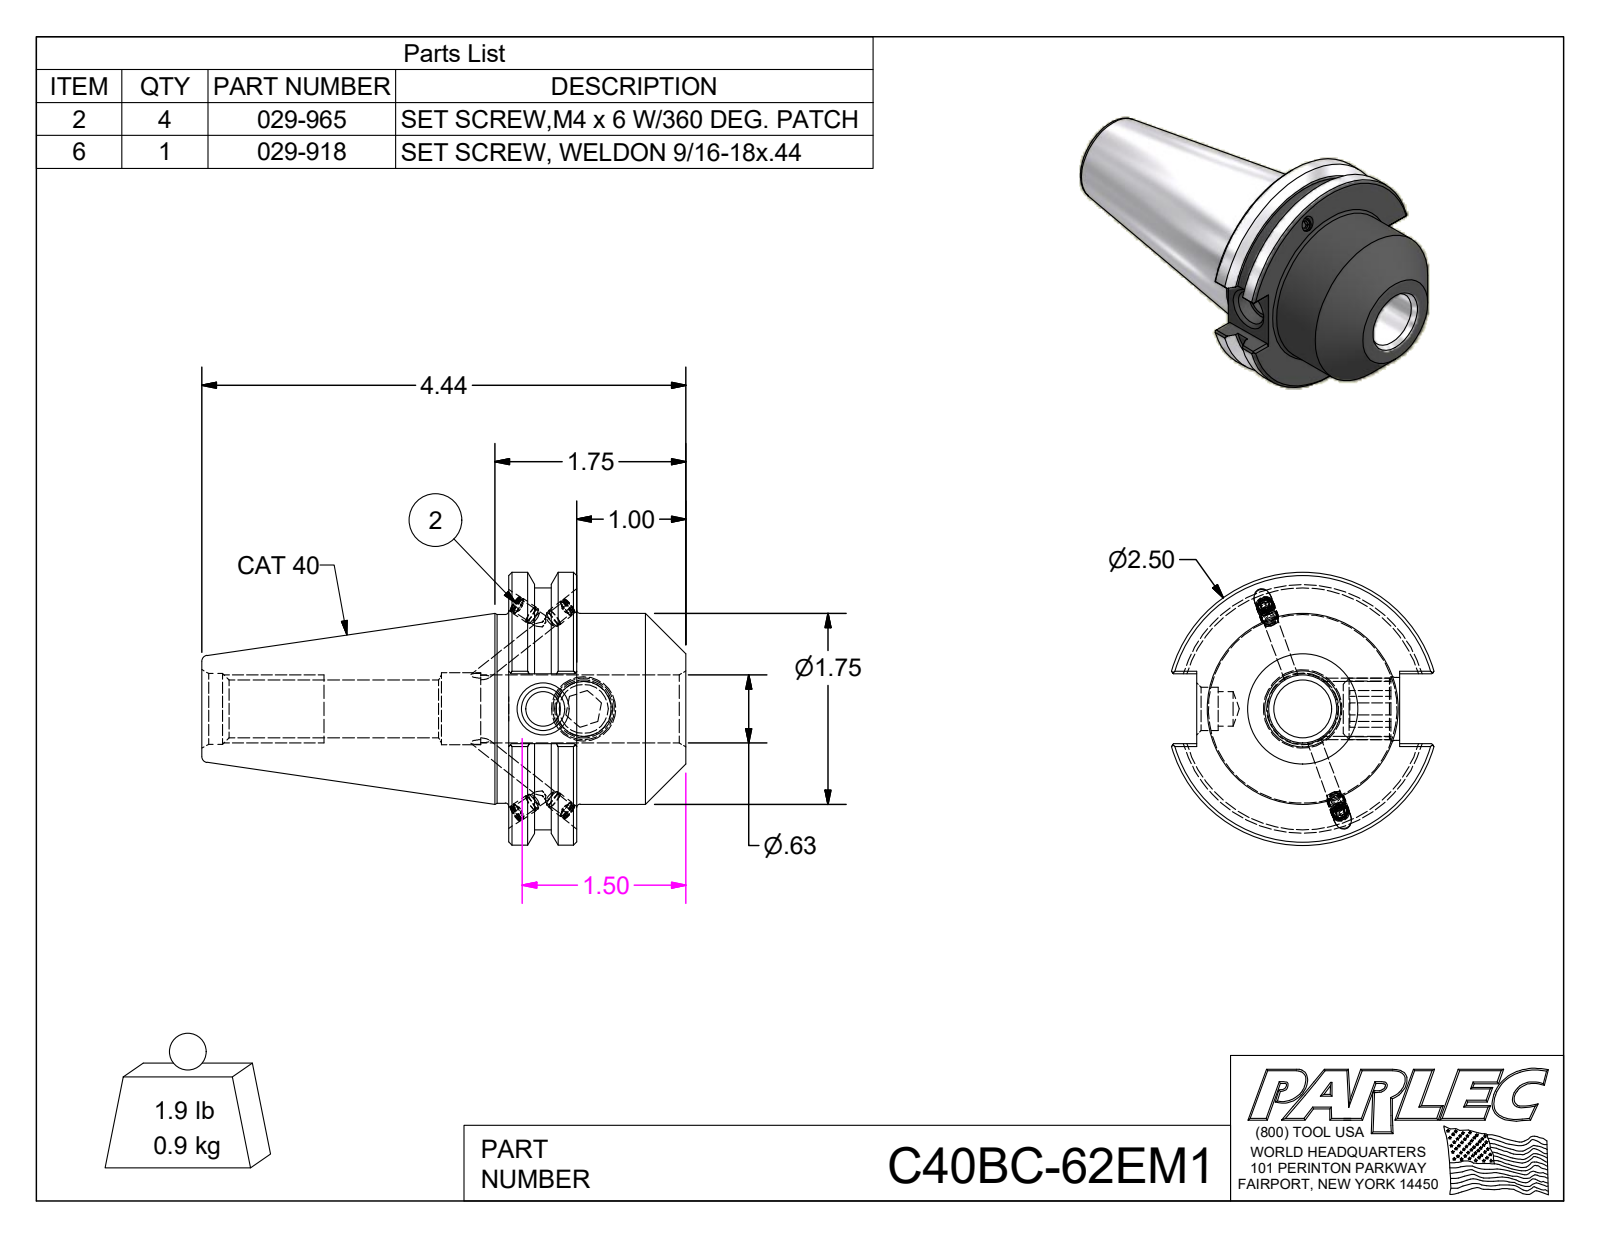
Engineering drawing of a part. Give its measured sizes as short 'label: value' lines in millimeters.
name: C40BC-62EM1; C40BC-62EM1-1; 029-918; 029-965
written by: Autodesk Inventor 2012 (AUTOMOTIVE_DESIGN)
unit: mm
bodies: 6 solids, 167 faces (87 planar, 36 cylindrical, 44 other)
size: 112.7 × 63.5 × 61
volume: 126 000 mm³; area: 26 810 mm²
holes: 4× ⌀3.3, 4× ⌀4.1, 1× ⌀8, 1× ⌀10.1, 1× ⌀12.8, 1× ⌀13.4, 1× ⌀15.9, 1× ⌀16.5, 1× ⌀16.8
bosses: 4× ⌀4.2, 4× ⌀4, 1× ⌀63.5, 1× ⌀56.4, 1× ⌀44.5, 1× ⌀43.9, 1× ⌀14.3
face distances: 15.9, 41.3, 25.4, 16.3, 47.2, 7.6, 71.5, 87.3, 112.7, 81.3
hole spacings: 9.4
